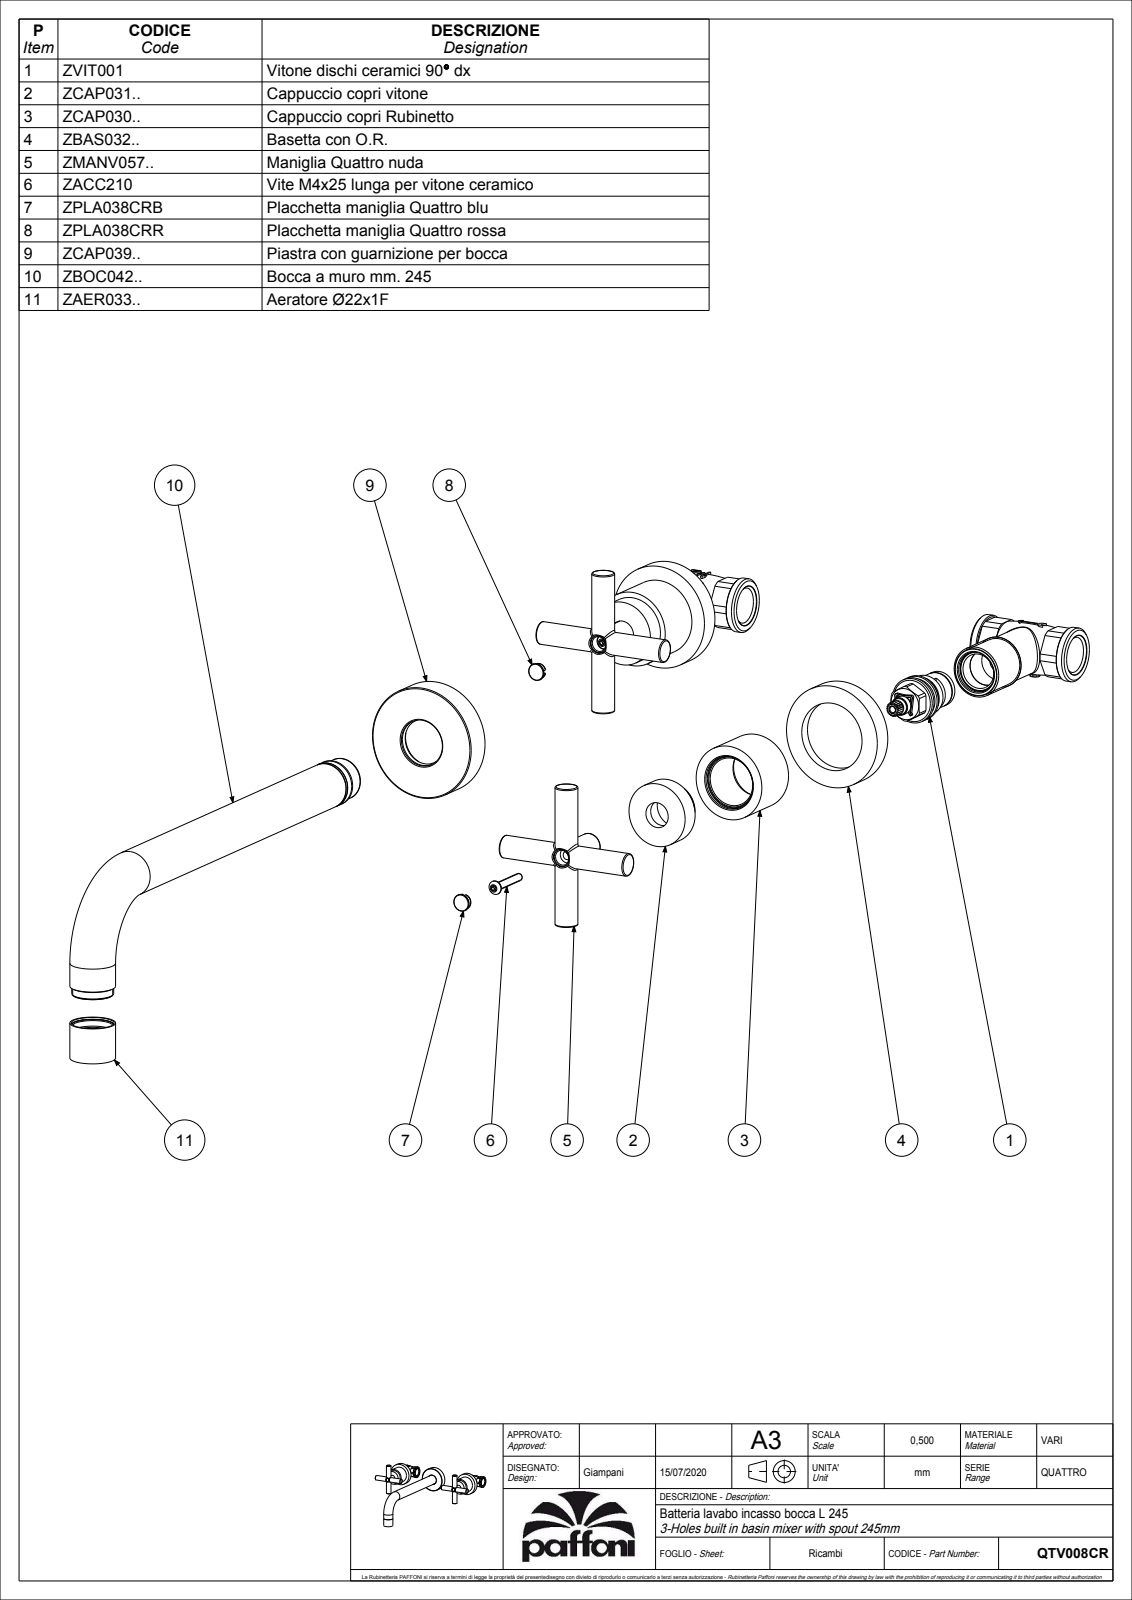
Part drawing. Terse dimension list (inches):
name: QTV008CR
written by: CREO PARAMETRIC BY PTC INC, 2020044 (CONFIG_CONTROL_DESIGN)
unit: in
bodies: 7 solids, 2272 faces (1818 planar, 254 cylindrical, 200 other)
size: 10.827 × 10.118 × 4.28
volume: 12.18 in³; area: 176.1 in²
holes: 4× ⌀0.827, 2× ⌀0.13, 2× ⌀0.177, 2× ⌀0.276, 2× ⌀0.315, 2× ⌀0.335, 2× ⌀0.346, 2× ⌀0.374, 2× ⌀0.406, 2× ⌀0.413, 2× ⌀0.531, 2× ⌀0.642
bosses: 3× ⌀0.472, 2× ⌀2.165, 2× ⌀1.929, 2× ⌀1.567, 2× ⌀1.417, 2× ⌀1.339, 2× ⌀1.063, 2× ⌀0.945
rounds: 34× R0.004, 4× R0.02, 4× R0.039, 2× R0.118, 2× R0.37
face distances: 0.157, 0.433, 0.591, 0.197, 0.059, 0.236, 0.098, 0.531, 0.394, 1.358
hole spacings: 3.937, 7.874
